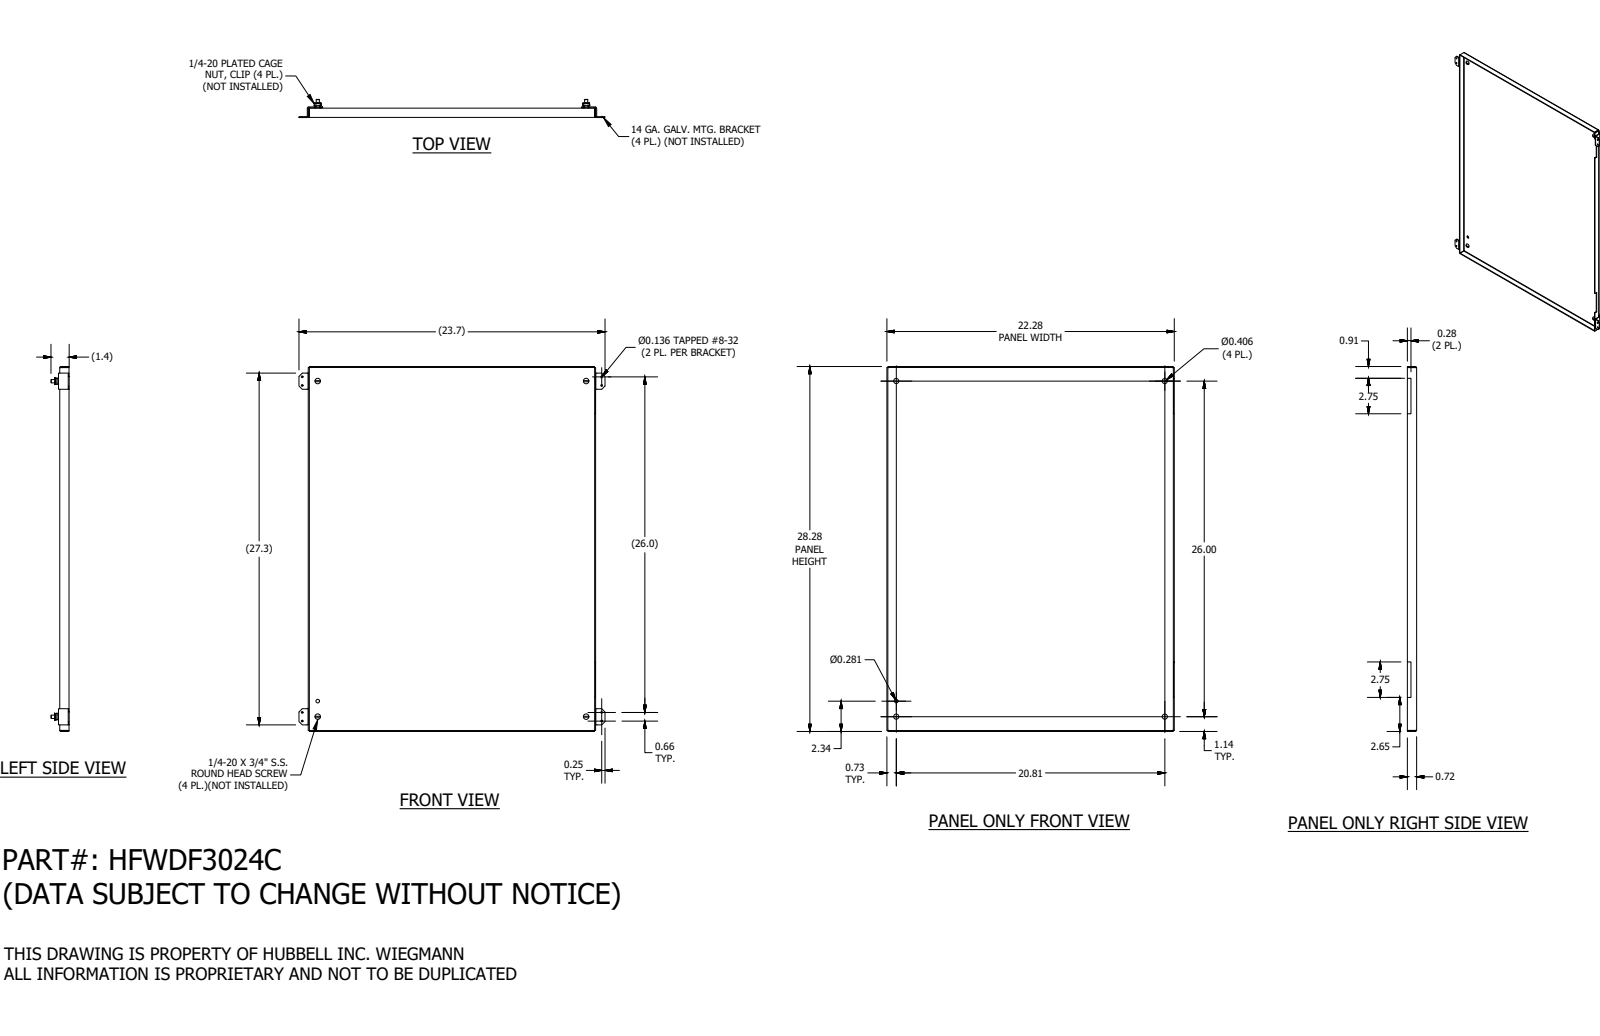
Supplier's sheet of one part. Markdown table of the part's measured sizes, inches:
| quantity | value |
| --- | --- |
| part name | HFWDF3024C |
| STEP written by | SolidWorks 2023 (AUTOMOTIVE_DESIGN) |
| units | inches |
| bodies | 13 solids, 599 faces (422 planar, 161 cylindrical, 16 other) |
| overall size | 28.281 × 23.726 × 1.415 |
| volume | 52.28 in³ |
| surface area | 1 425 in² |
| round holes (diameter × count) | 0.136 × 8, 0.185 × 4, 0.328 × 4, 0.406 × 4, 0.281 × 1 |
| round bosses / shafts (diameter × count) | 0.25 × 4 |
| partial cylindrical surfaces (radius × count) | 0.025 × 20, 0.021 × 16, 0.045 × 12, 0.031 × 8, 0.105 × 8, 0.021 × 4 |
| main face-to-face distances | 0.074, 22.207, 28.207, 22.281, 22.133, 28.133, 28.281, 0.094, 0.719, 0.645 |
| hole center spacings | 1.251, 22.022, 26, 0.66, 23.227, 23.236, 25.698, 26.357 |
